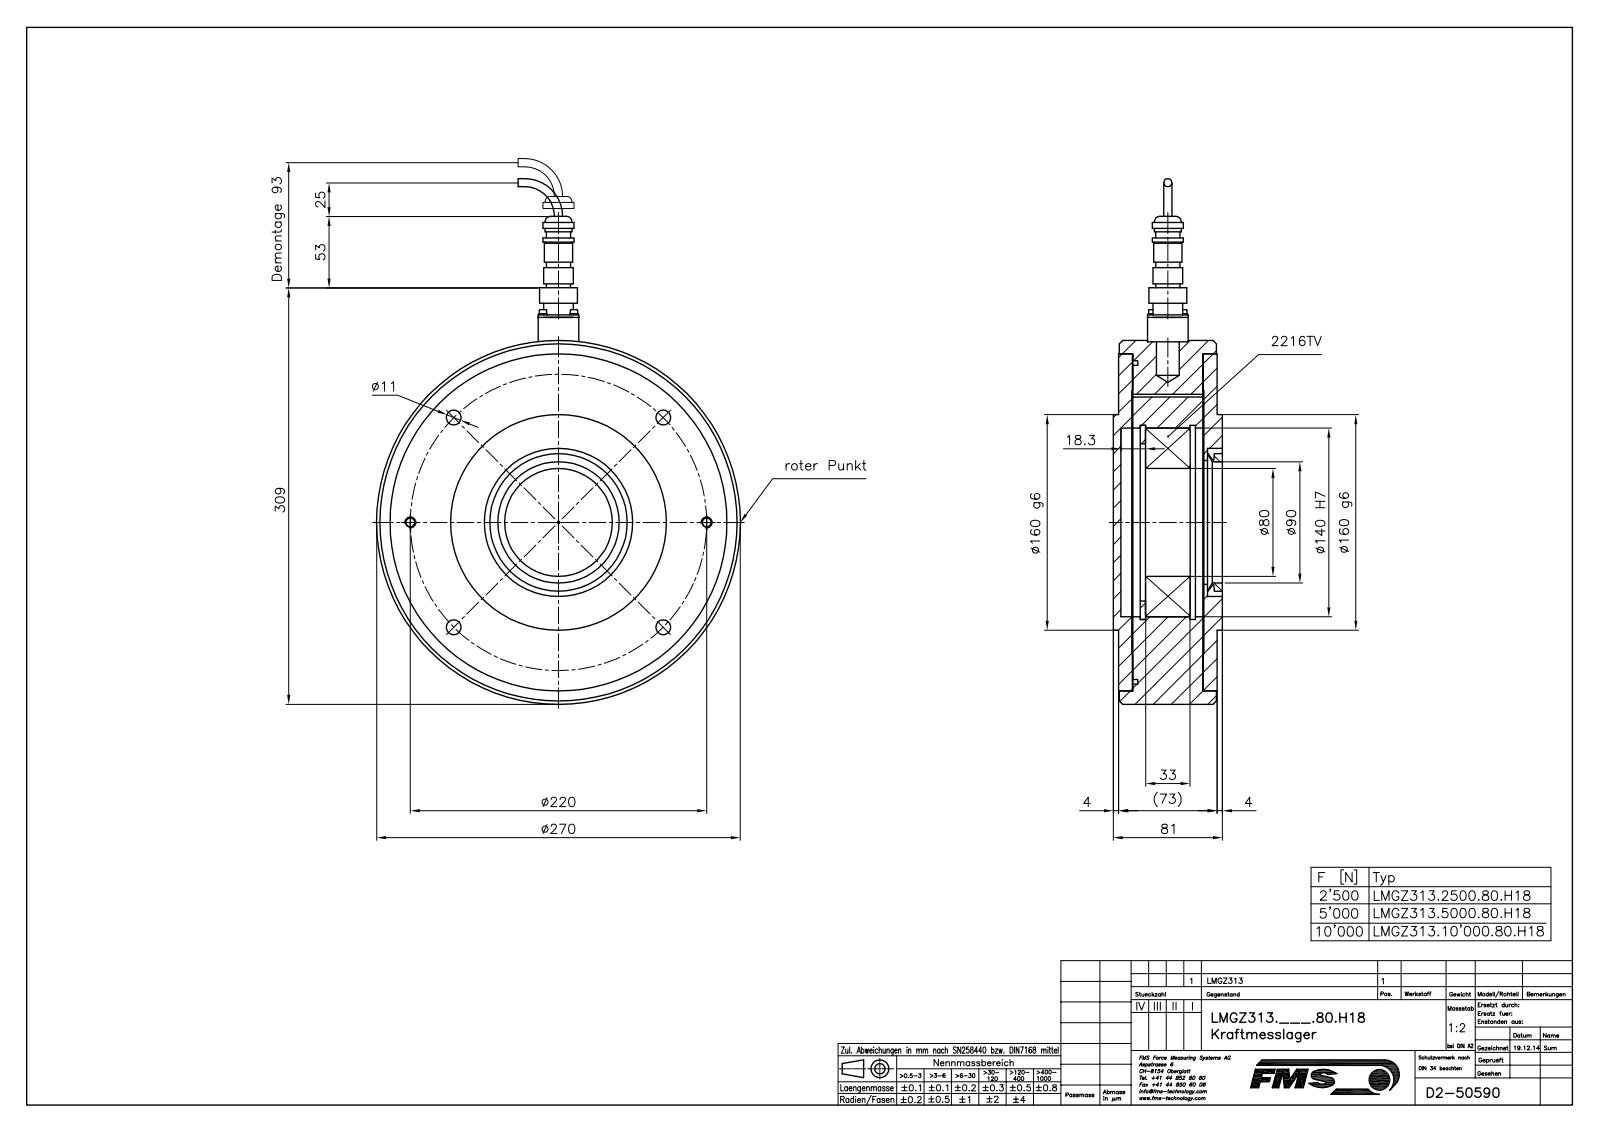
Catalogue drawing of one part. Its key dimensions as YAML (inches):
part_name: "L50590_STP; L4899004; TEIL1; L49342 (+7 more)"
step_written_by: "Mechanical Desktop 2009 (CONFIG_CONTROL_DESIGN)"
units: inches
bodies: {solids: 8, faces: 241, planar: 61, cylindrical: 146, other: 34}
overall_size: [15.354, 12.61, 10.63]
volume: 219.9
surface_area: 758
round_holes:
  - {diameter: 0.102, count: 4}
  - {diameter: 0.126, count: 4}
  - {diameter: 0.134, count: 4}
  - {diameter: 0.433, count: 4}
  - {diameter: 0.272, count: 2}
  - {diameter: 0.354, count: 2}
  - {diameter: 0.591, count: 2}
  - {diameter: 0.669, count: 1}
  - {diameter: 3.15, count: 1}
  - {diameter: 3.543, count: 1}
  - {diameter: 3.622, count: 1}
  - {diameter: 4.331, count: 1}
round_bosses_or_shafts:
  - {diameter: 0.098, count: 4}
  - {diameter: 10.63, count: 1}
  - {diameter: 9.173, count: 1}
  - {diameter: 6.299, count: 1}
  - {diameter: 4.016, count: 1}
  - {diameter: 1.102, count: 1}
  - {diameter: 0.906, count: 1}
  - {diameter: 0.866, count: 1}
partial_cylinders:
  - {radius: 0.157, count: 4}
face_to_face_distances: [0.382, 0.402, 2.083, 0.409, 2.457, 0.157, 2.484, 0.028, 2.075, 0.559]
hole_center_spacings: [4.331, 0.64, 0.906, 3.315, 6.124, 8.002, 8.661, 1.281]
